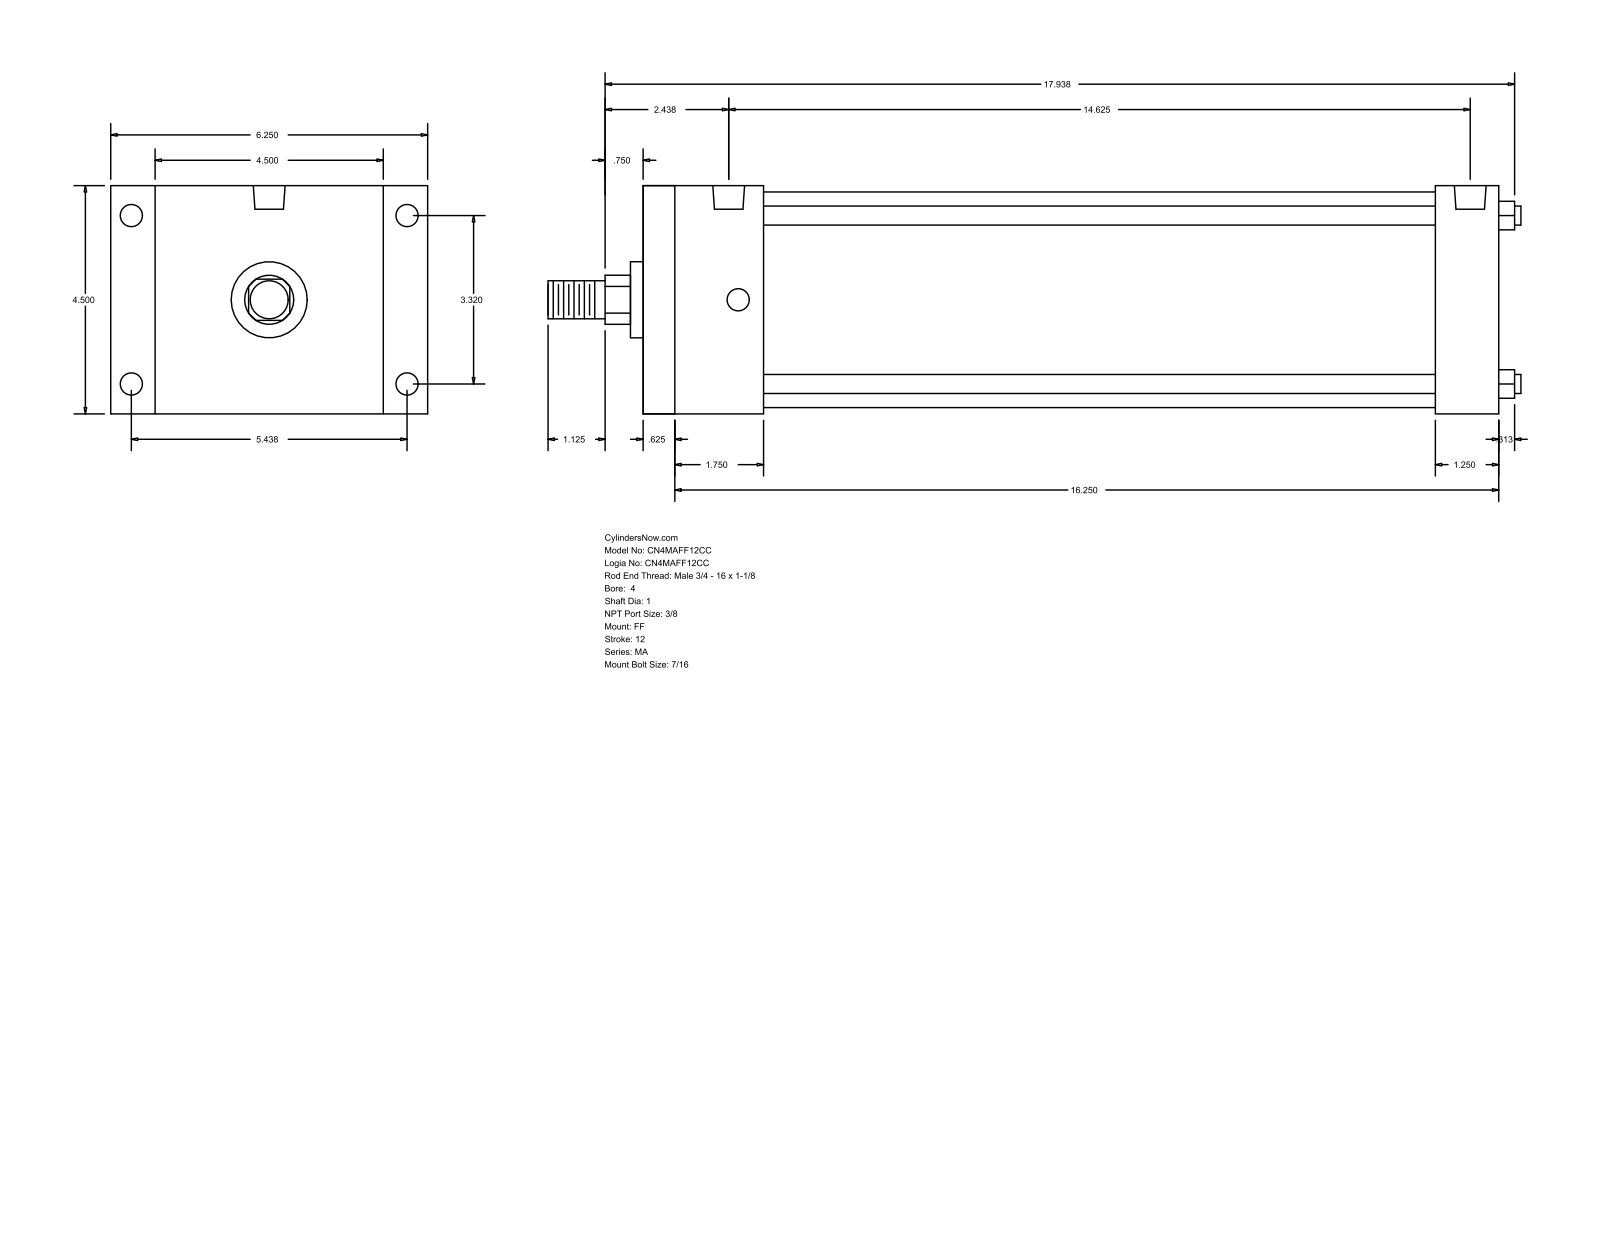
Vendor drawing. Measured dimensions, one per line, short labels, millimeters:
name: MA_FF__0400_1
written by: GSSL Pune (CONFIG_CONTROL_DESIGN)
unit: mm
bodies: 0 solids, 92 faces (64 planar, 28 cylindrical, 0 other)
size: 487.36 × 158.75 × 114.3
holes: 8× ⌀11.11, 2× ⌀15.93
bosses: 4× ⌀9.53, 1× ⌀107.95, 1× ⌀38.1, 1× ⌀25.4, 1× ⌀19.05
rounds: 1× R12.29
face distances: 114.3, 428.63, 15.87, 412.76, 22.23, 136.53, 396.88, 381.01, 31.75, 60.33
hole spacings: 84.32, 138.12, 161.82, 361.95, 4.76, 4.77, 366.71, 366.72
